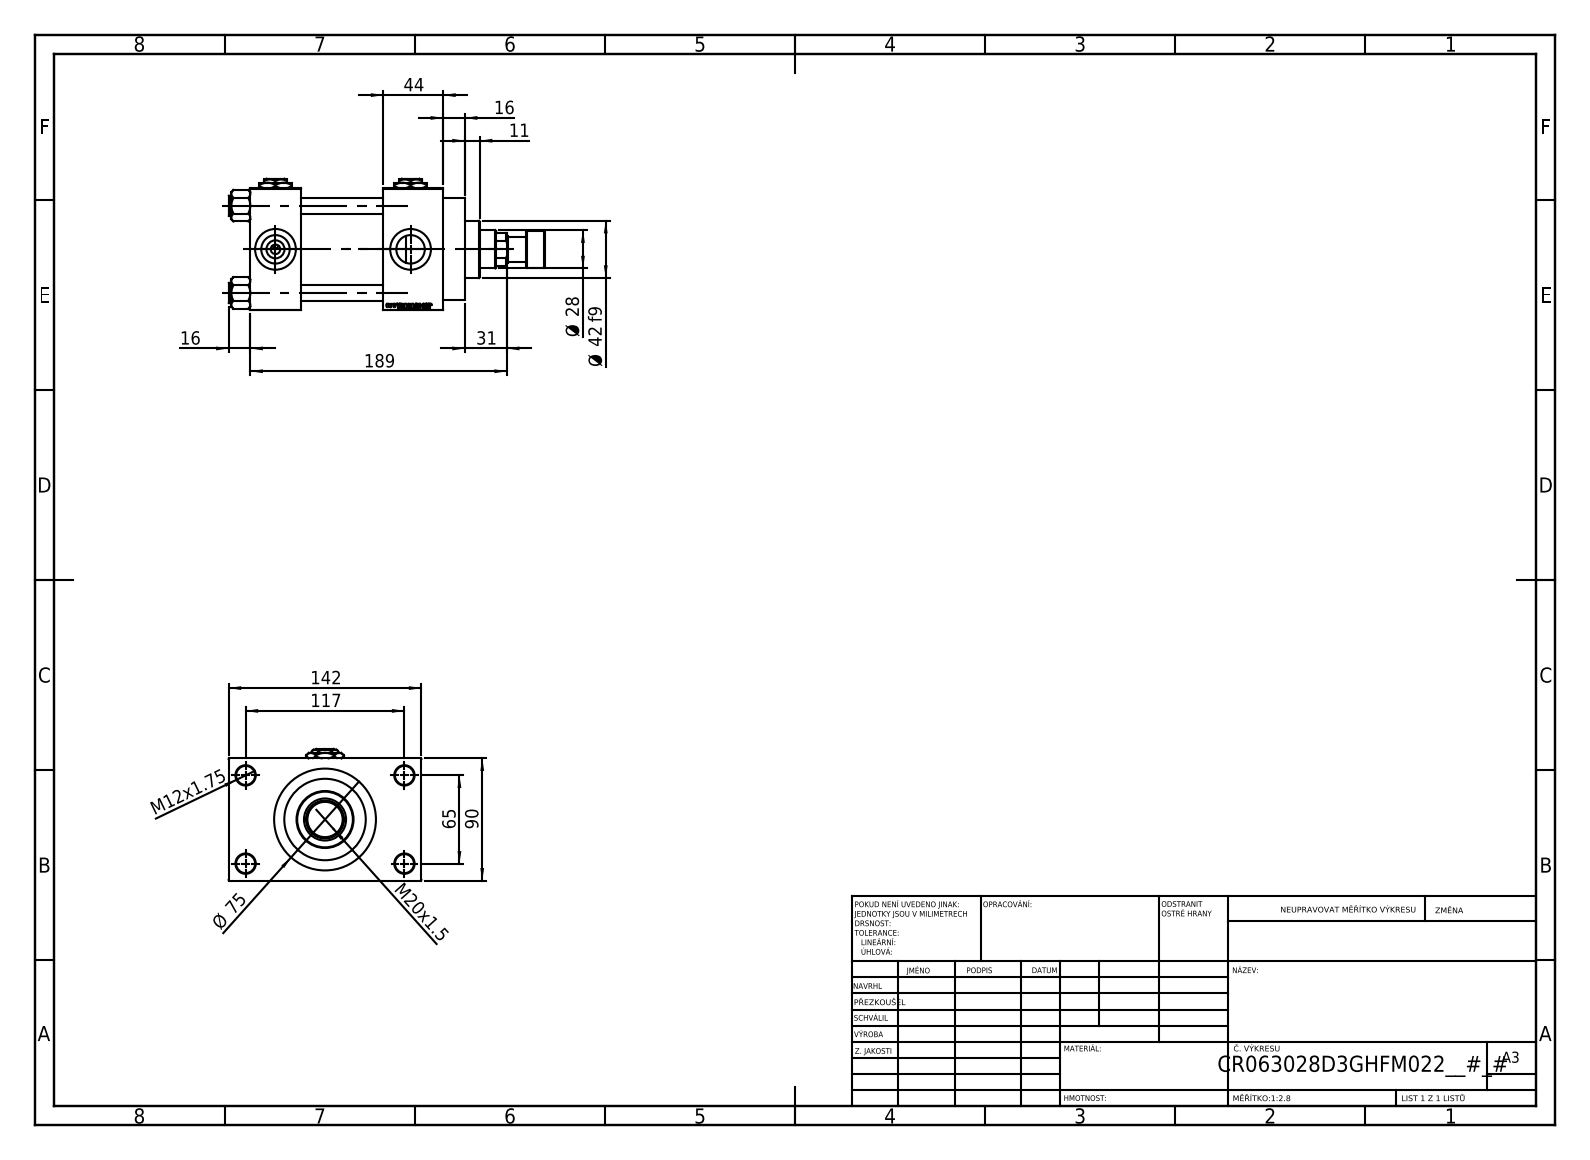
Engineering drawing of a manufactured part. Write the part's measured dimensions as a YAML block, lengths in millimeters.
part_name: "V215CR_ROD_END_F; V215_VC_A; NUT_M5_D; V215CR_VCP_D (+3 more)"
step_written_by: "SolidWorks 2019 (CONFIG_CONTROL_DESIGN)"
units: millimeters
bodies: {solids: 14, faces: 1218, planar: 549, cylindrical: 103, other: 566}
overall_size: [233, 142, 97]
volume: 1106000
surface_area: 209505
round_holes:
  - {diameter: 12, count: 4}
  - {diameter: 14, count: 4}
  - {diameter: 20.96, count: 4}
  - {diameter: 30, count: 4}
  - {diameter: 7, count: 3}
  - {diameter: 18.5, count: 1}
  - {diameter: 28, count: 1}
  - {diameter: 31, count: 1}
  - {diameter: 50, count: 1}
  - {diameter: 60, count: 1}
  - {diameter: 63, count: 1}
round_bosses_or_shafts:
  - {diameter: 15, count: 4}
  - {diameter: 75, count: 1}
  - {diameter: 69, count: 1}
  - {diameter: 42, count: 1}
  - {diameter: 27, count: 1}
  - {diameter: 18, count: 1}
face_to_face_distances: [90, 142, 61, 37, 98, 105, 44, 26, 116, 16]
hole_center_spacings: [26.35, 45.47, 64.3, 66.92, 69.81, 90.65, 111.34, 65]
